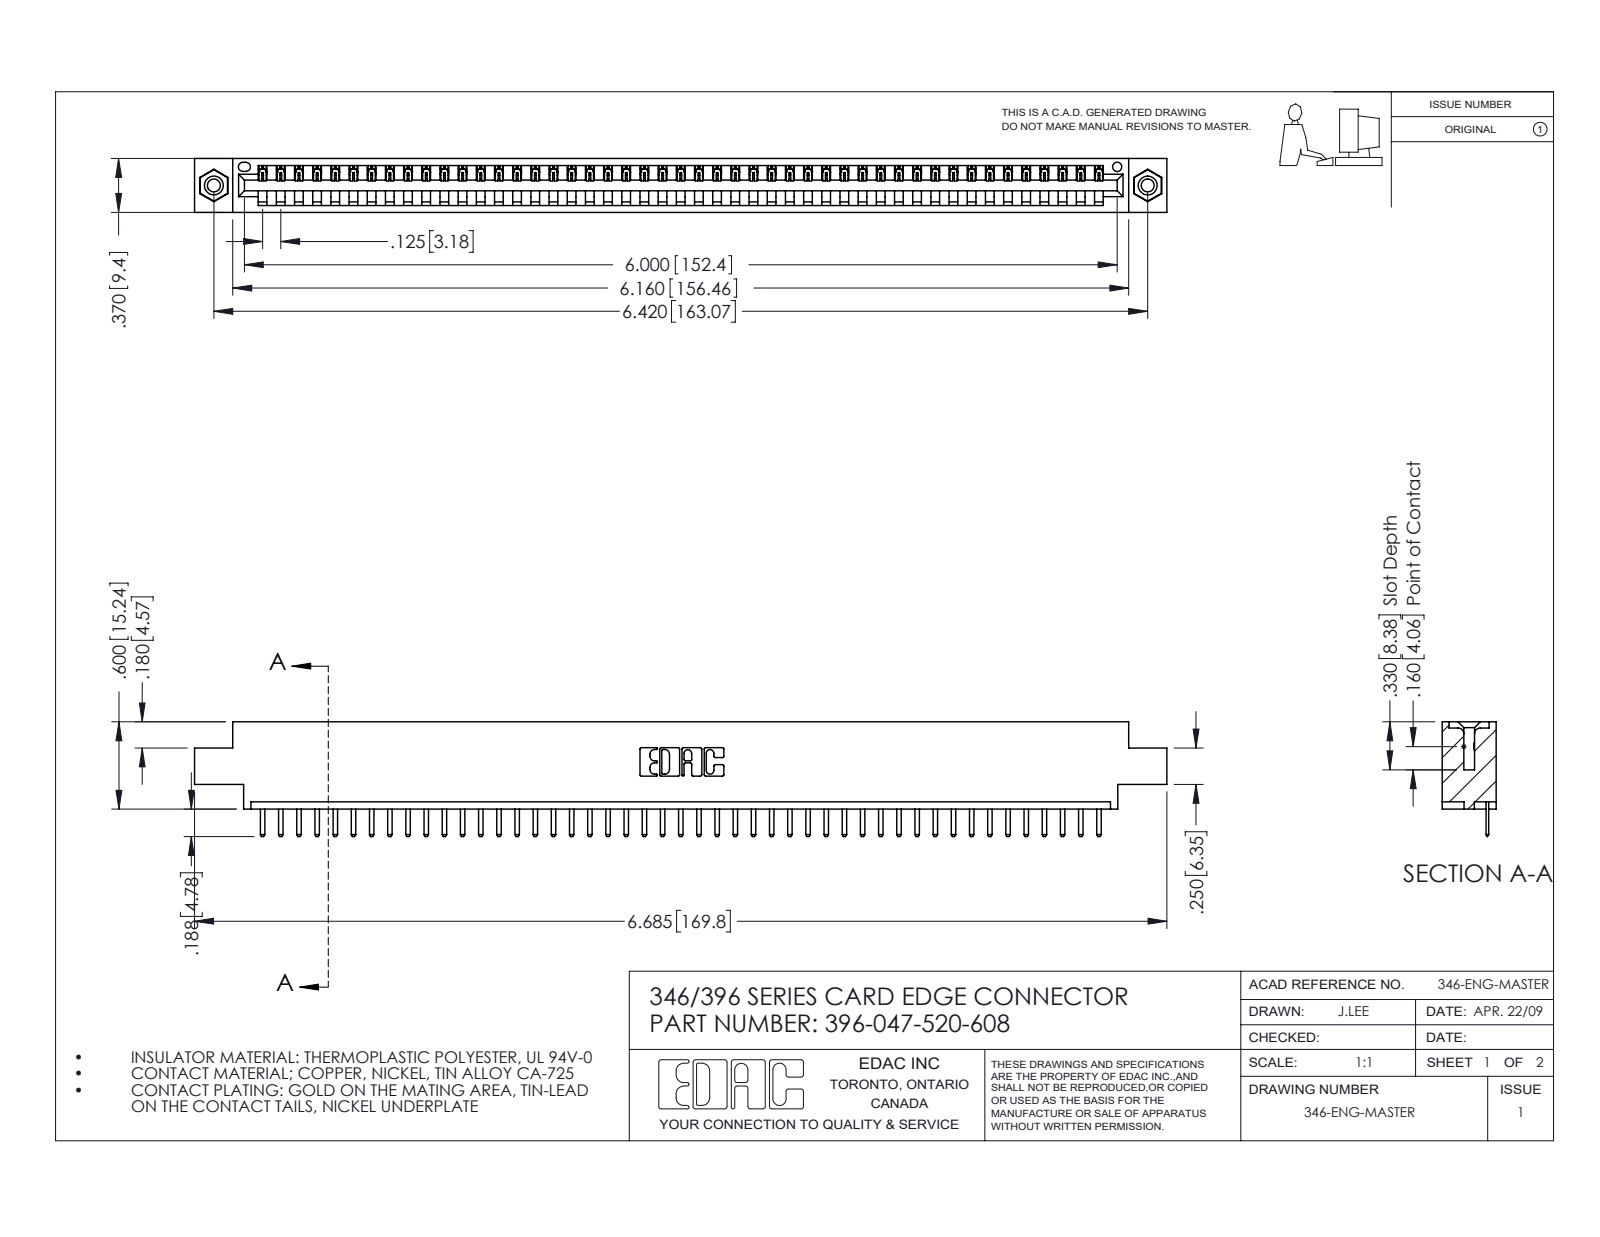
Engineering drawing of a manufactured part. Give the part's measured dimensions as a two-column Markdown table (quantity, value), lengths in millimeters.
| quantity | value |
| --- | --- |
| part name | 396-047-520-608; 345-250-001_345-250-003-102; 346 Part_0.170 Offset - 0.156 Dia-TI; 345-292-001_345-293-120 |
| STEP written by | SolidWorks 2016 (CONFIG_CONTROL_DESIGN) |
| units | millimeters |
| bodies | 50 solids, 3100 faces (2086 planar, 998 cylindrical, 16 other) |
| overall size | 169.8 × 20 × 9.4 |
| volume | 16 000 mm³ |
| surface area | 19 770 mm² |
| round holes (diameter × count) | 2.3 × 2, 3.2 × 2, 4 × 2, 1.6 × 1 |
| round bosses / shafts (diameter × count) | 3.9 × 2 |
| partial cylindrical surfaces (radius × count) | 0.3 × 96, 0.2 × 94, 0.3 × 22, 0.2 × 6, 0.8 × 6, 0.7 × 3, 0.8 × 2, 1 × 2 |
| main face-to-face distances | 1.2, 8.2, 9.4, 6.4, 5.6, 3.8, 2.5, 4.4, 1.8, 7.6 |
| hole center spacings | 6.2, 157.8, 163.1 |
